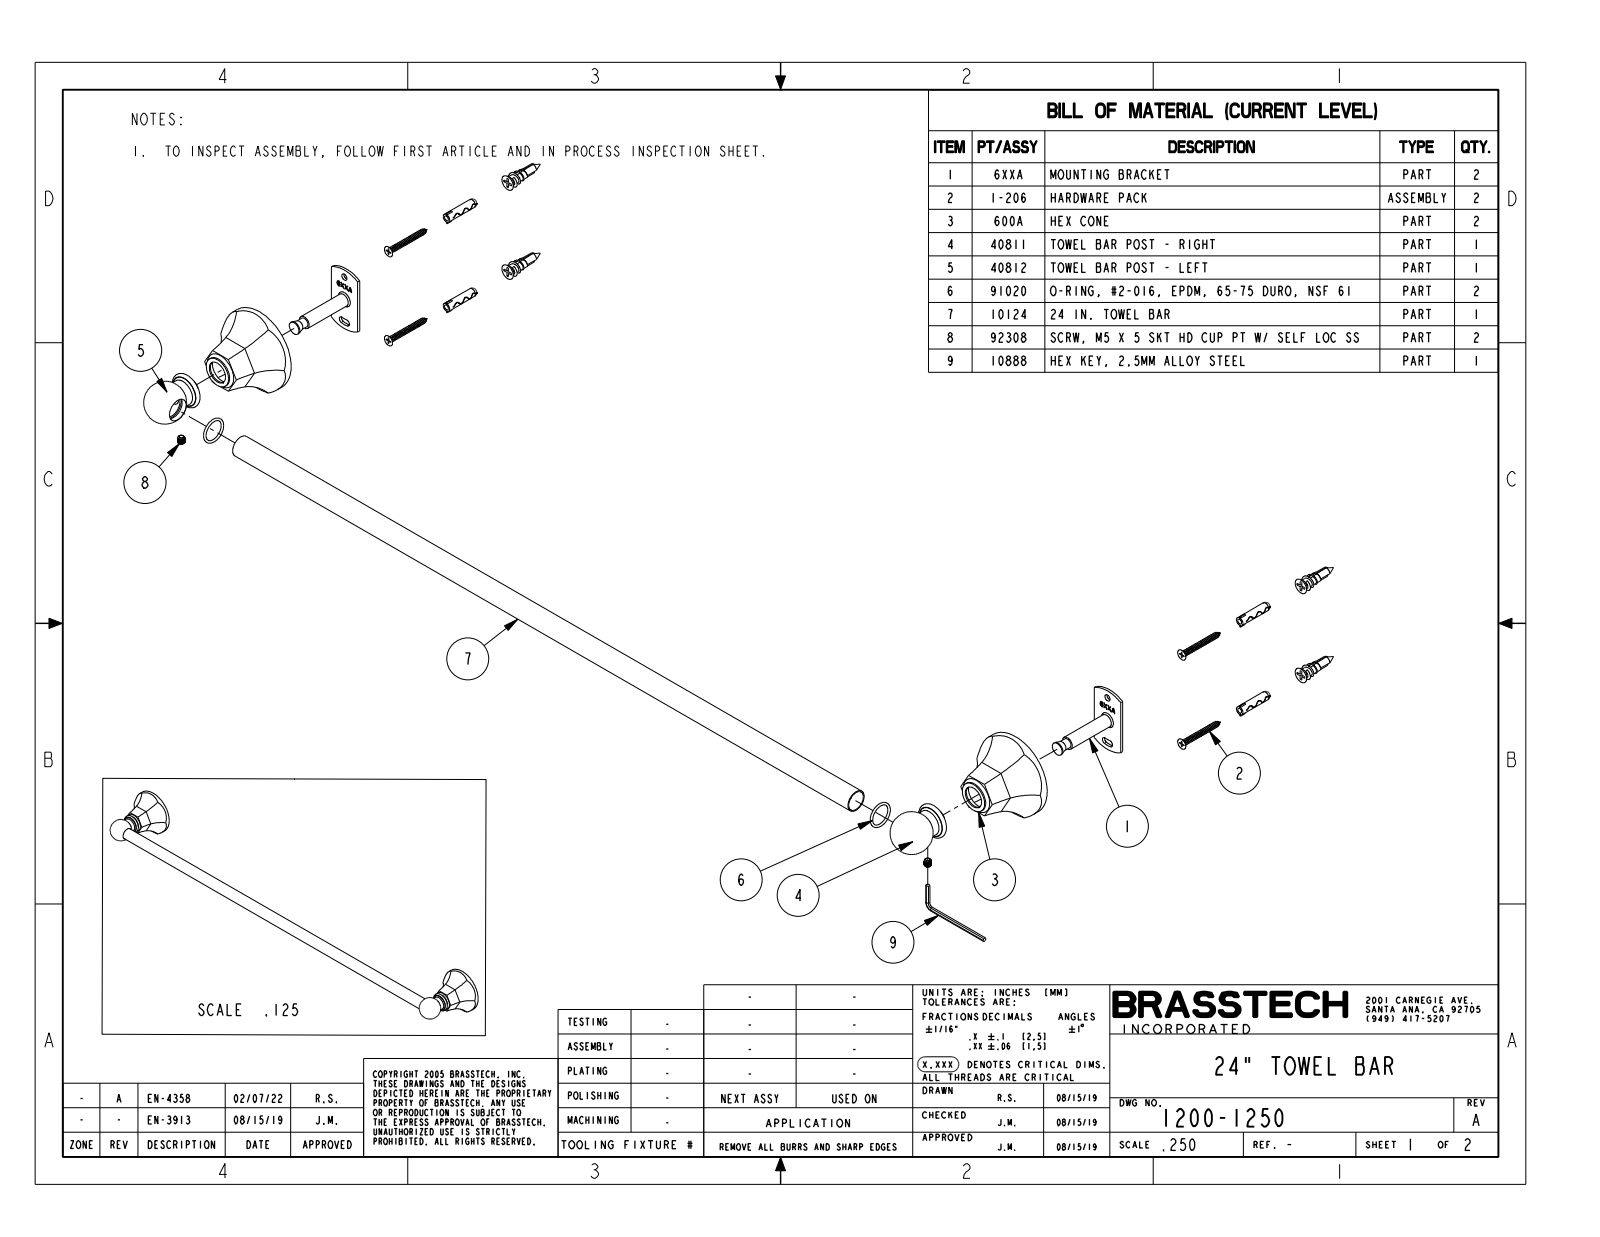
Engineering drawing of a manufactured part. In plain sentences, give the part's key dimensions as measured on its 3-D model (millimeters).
The part is named "1200-1250". Its 3-D file was written by "CREO PARAMETRIC BY PTC INC, 2018400 (AUTOMOTIVE_DESIGN)". It is 1 solid with 62 faces: 8 planar, 38 cylindrical and 16 other. Overall it measures 672.1 by 78.9 by 62.5 millimeters. Its volume is 266 100 cubic millimeters and its surface area 54 720 square millimeters. Round bosses or shafts: 2 of diameter 62.5, 2 of diameter 22, 2 of diameter 19.1, 1 of diameter 15.9. Partial cylindrical surfaces (rounded edges, fillets, slot ends): 10 of radius 33, 10 of radius 116.9. The main face-to-face distances are 38.5, 41.5, 3, 45, 6.5, 3.5.
